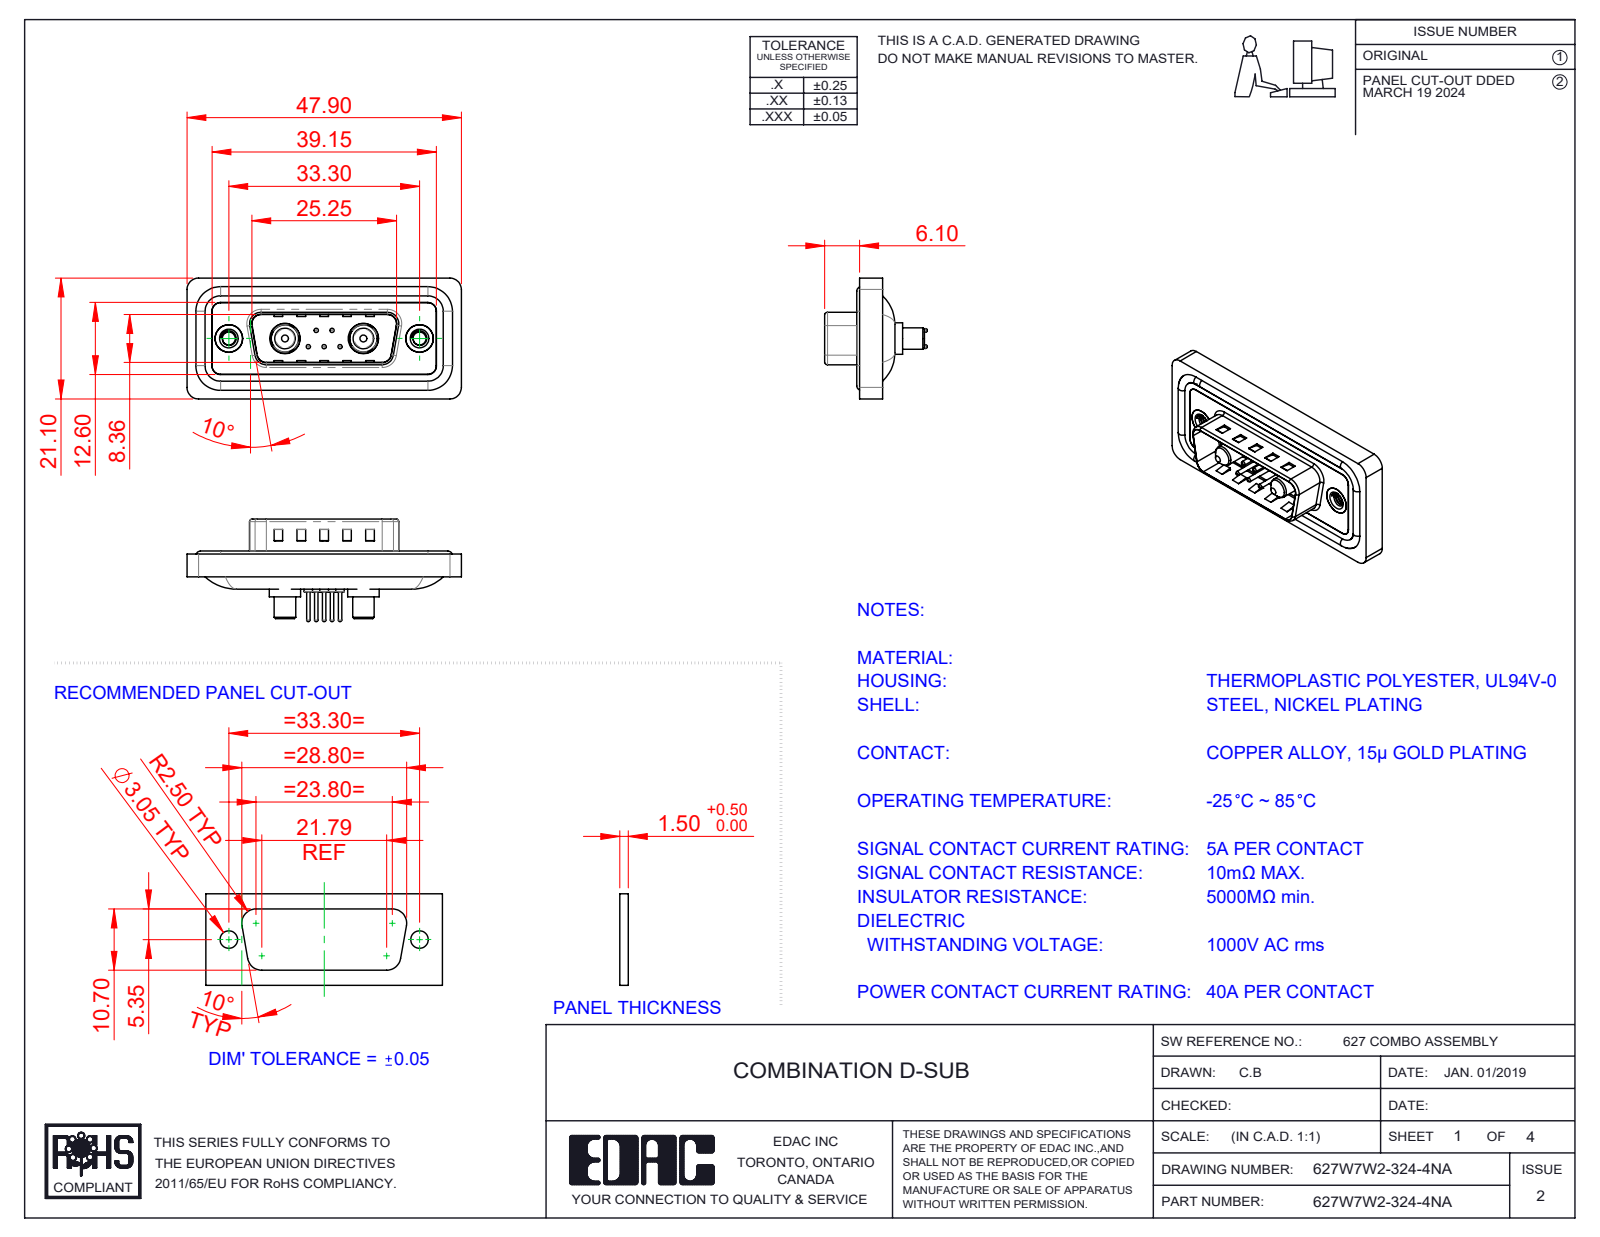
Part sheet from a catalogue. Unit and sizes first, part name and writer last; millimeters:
Units: millimetres
Overall size (bounding box): 47.9 × 21.1 × 17.9
Round holes (diameter × count): ⌀0.75 ×5, ⌀1.6 ×5, ⌀2 ×5, ⌀2.26 ×2, ⌀4 ×2, ⌀4.8 ×2, ⌀4.85 ×2, ⌀5 ×2, ⌀5.3 ×2
Round bosses / shafts (diameter × count): ⌀1.5 ×5, ⌀0.6 ×5, ⌀1.6 ×4, ⌀5.5 ×2, ⌀5.2 ×2, ⌀4.9 ×2, ⌀4.75 ×2, ⌀3.75 ×2
Partial cylindrical surfaces — rounded edges, fillets, slot ends (radius × count): R1.5 ×26, R2 ×20, R0.5 ×8, R1.6 ×8, R0.25 ×4, R0.6 ×4, R0.65 ×4, R0.9 ×4
Main face-to-face distances: 0.4, 1.1, 1.6, 1.5, 0.5, 3.1, 2.9, 0.82, 9.58, 2.5
Hole centre spacings: 3.16, 2.77, 9.8, 23.5, 4.31, 4.33, 5.03, 5.04
Volume: 5 555 mm³ · Surface area: 8 812 mm²
Bodies: 16 solids, 708 faces (232 planar, 294 cylindrical, 182 other)
Part name (STEP PRODUCT): 627Combo Contact Row 1_24; 627W7W2-324-4NA; 627Combo Shell Rear_15 Contacts; 627Combo Housing_7W2 (+5 more)
STEP written by: SolidWorks 2023 (CONFIG_CONTROL_DESIGN)
